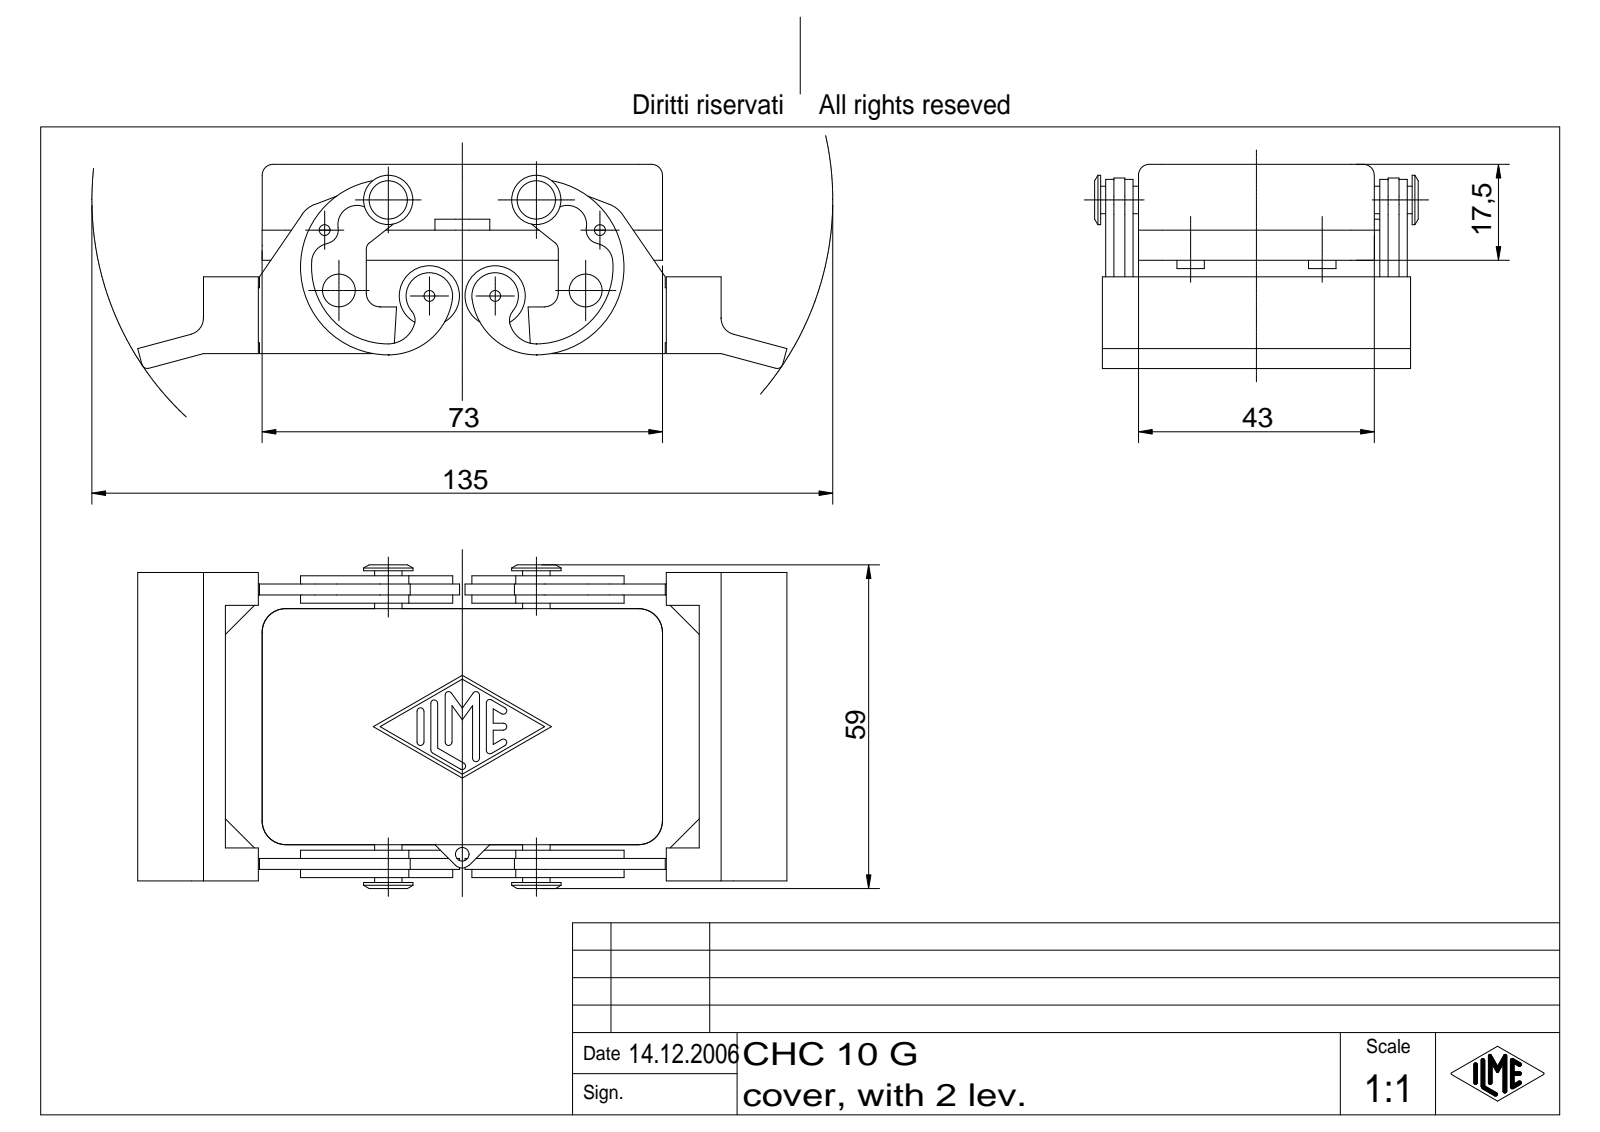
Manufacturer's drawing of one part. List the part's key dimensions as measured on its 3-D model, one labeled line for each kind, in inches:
Part name (STEP PRODUCT): CHC 10 G
STEP written by: Autodesk Inventor 7 (AUTOMOTIVE_DESIGN)
Units: inches
Bodies: 1 solid, 501 faces (165 planar, 153 cylindrical, 183 other)
Overall size (bounding box): 4.661 × 2.323 × 1.465
Volume: 2.824 in³ · Surface area: 48.07 in²
Round holes (diameter × count): ⌀0.079 ×4, ⌀0.098 ×3, ⌀0.236 ×1
Round bosses / shafts (diameter × count): ⌀0.433 ×2, ⌀0.354 ×2, ⌀0.197 ×2
Partial cylindrical surfaces — rounded edges, fillets, slot ends (radius × count): R0.024 ×14, R0.079 ×10, R0.169 ×8, R0.098 ×6, R0.138 ×4, R0.197 ×4, R0.039 ×2, R0.059 ×2
Main face-to-face distances: 0.177, 0.118, 1.516, 1.693, 0.098, 0.276, 1.969, 0.689, 0.571, 0.059
Hole centre spacings: 0.888, 1.312, 0.445, 0.472, 0.651, 1.123, 1.923, 1.976
